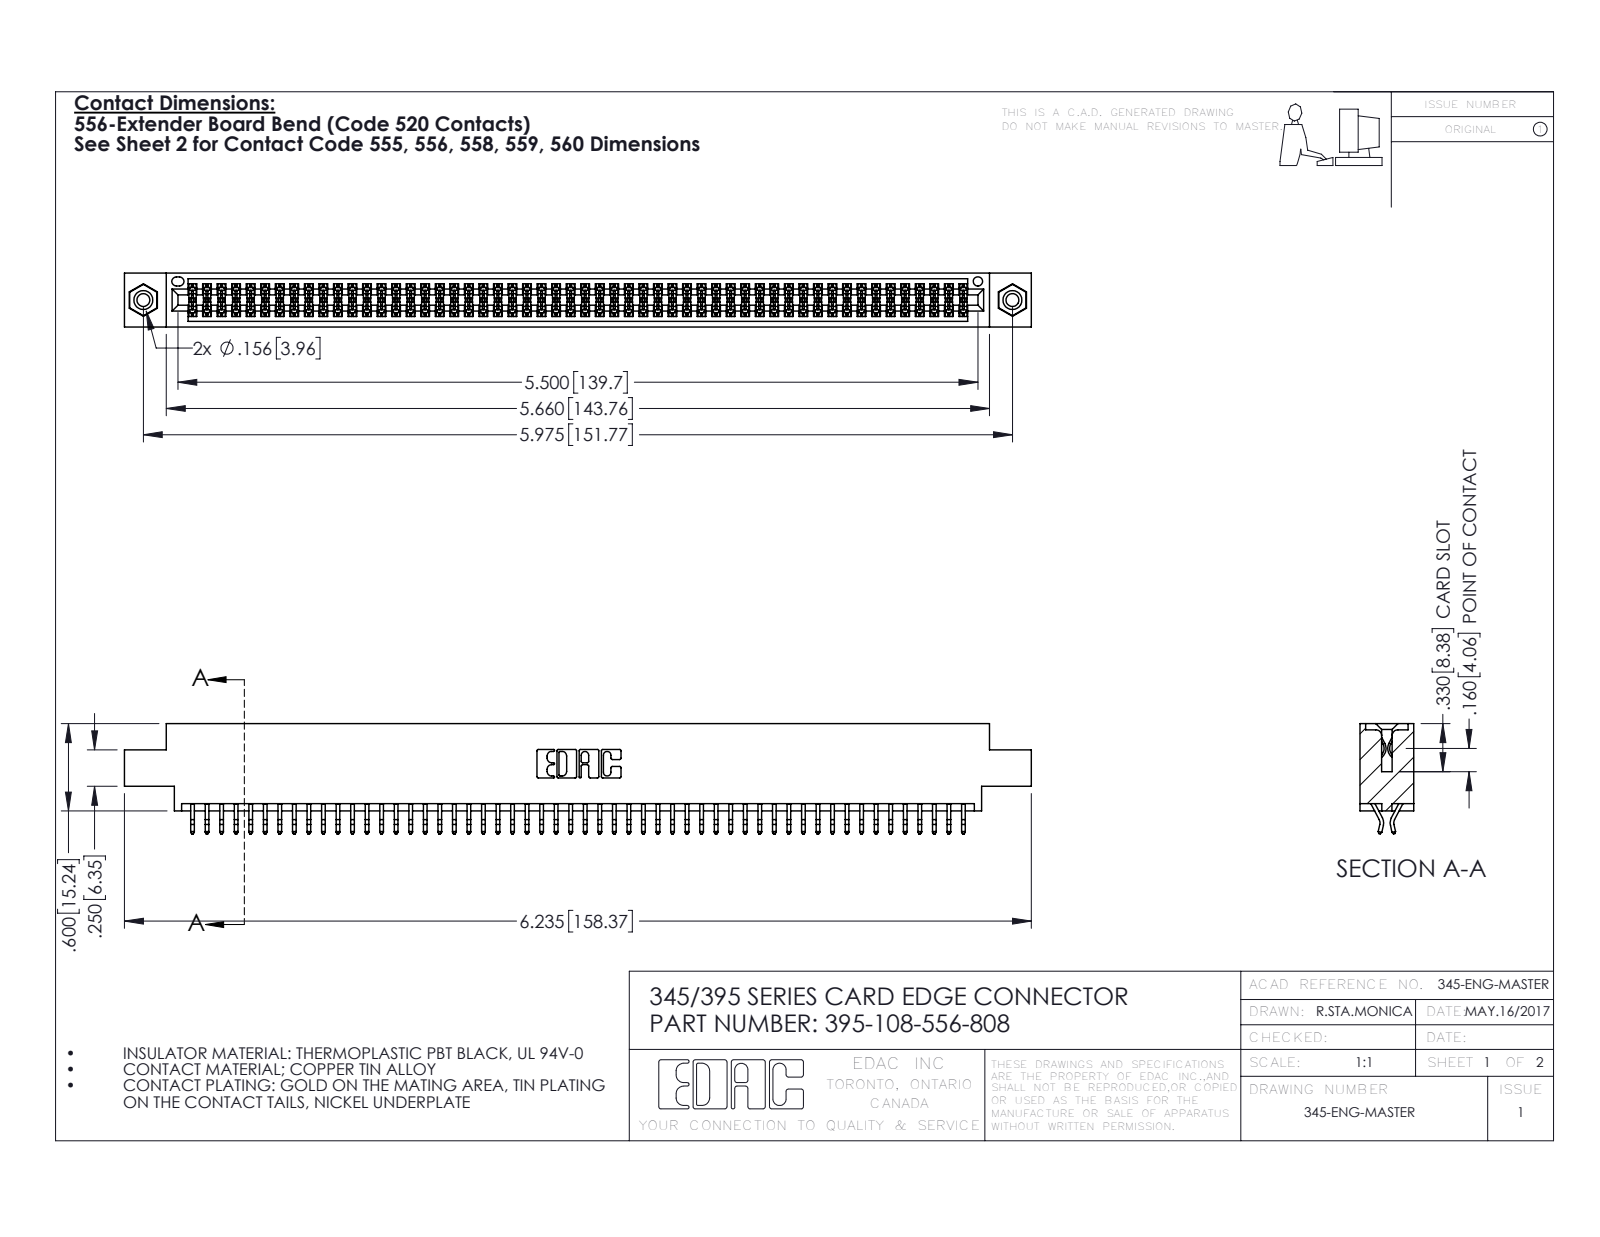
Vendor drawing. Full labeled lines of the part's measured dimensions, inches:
Part name (STEP PRODUCT): 345-292-001_556 Tail; 345 Part_0.170 Offset - 0.156 Dia-TI; 395-108-556-808; 345-250-001_345-250-003-102
STEP written by: SolidWorks 2016 (CONFIG_CONTROL_DESIGN)
Units: inches
Bodies: 111 solids, 6238 faces (4112 planar, 2110 cylindrical, 16 other)
Overall size (bounding box): 6.235 × 0.757 × 0.37
Volume: 0.938 in³ · Surface area: 35.68 in²
Round holes (diameter × count): ⌀0.089 ×2, ⌀0.125 ×2, ⌀0.156 ×2, ⌀0.064 ×1
Round bosses / shafts (diameter × count): ⌀0.155 ×2
Partial cylindrical surfaces — rounded edges, fillets, slot ends (radius × count): R0.006 ×162, R0.01 ×22, R0.007 ×6, R0.031 ×6, R0.026 ×3, R0.01 ×2, R0.014 ×2, R0.019 ×2
Main face-to-face distances: 0.072, 0.298, 0.37, 0.025, 0.2, 0.098, 0.272, 0.225, 0.175, 0.149
Hole centre spacings: 0.27, 5.739, 5.975
